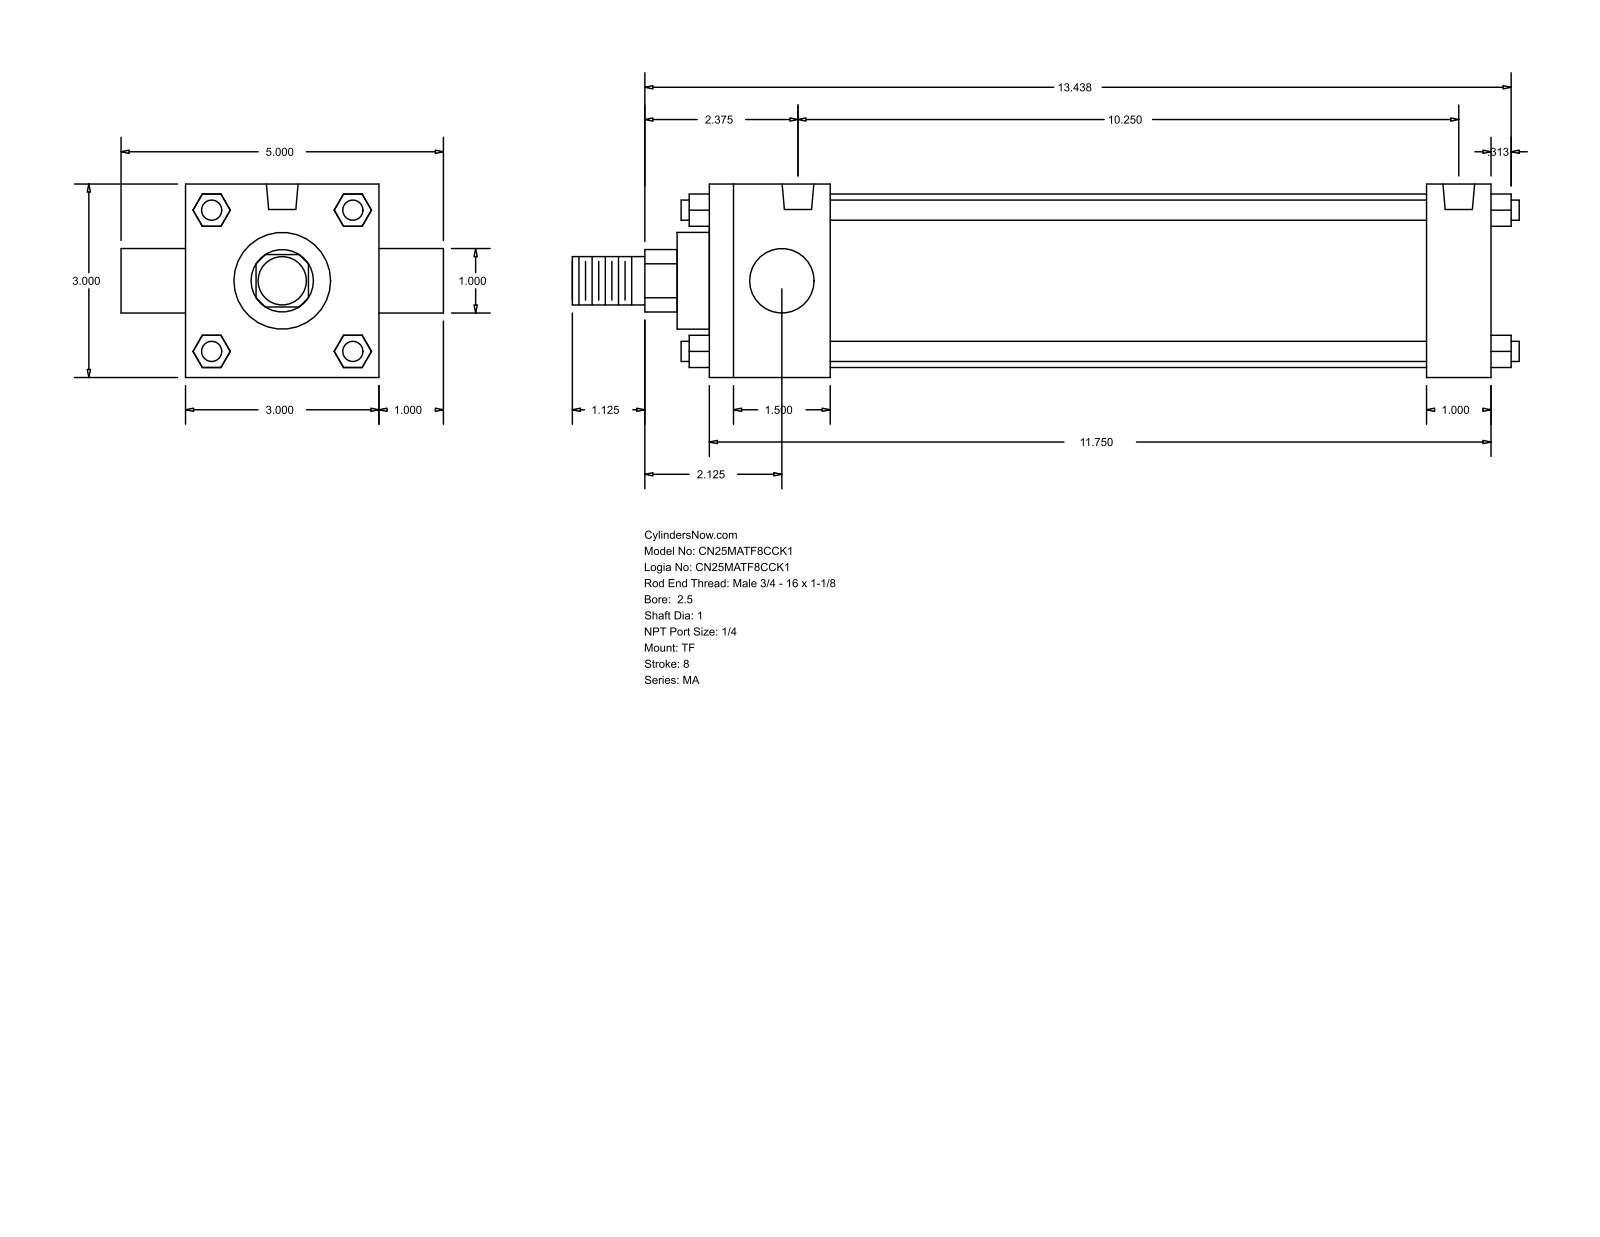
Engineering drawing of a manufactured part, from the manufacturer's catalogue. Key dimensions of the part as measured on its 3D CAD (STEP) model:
Part name (STEP PRODUCT): MA_TF__0250_1
STEP written by: GSSL Pune (CONFIG_CONTROL_DESIGN)
Units: millimetres
Bodies: 0 solids, 120 faces (92 planar, 28 cylindrical, 0 other)
Overall size (bounding box): 373.06 × 127 × 76.2
Round holes (diameter × count): ⌀7.94 ×3, ⌀12.49 ×2
Round bosses / shafts (diameter × count): ⌀7.94 ×4, ⌀25.4 ×2, ⌀68.33 ×1, ⌀38.1 ×1, ⌀19.05 ×1
Partial cylindrical surfaces — rounded edges, fillets, slot ends (radius × count): R12.29 ×1
Main face-to-face distances: 76.2, 307.98, 25.4, 12.7, 47.63, 282.58, 234.95, 260.35, 101.6, 27.81
Hole centre spacings: 260.35
